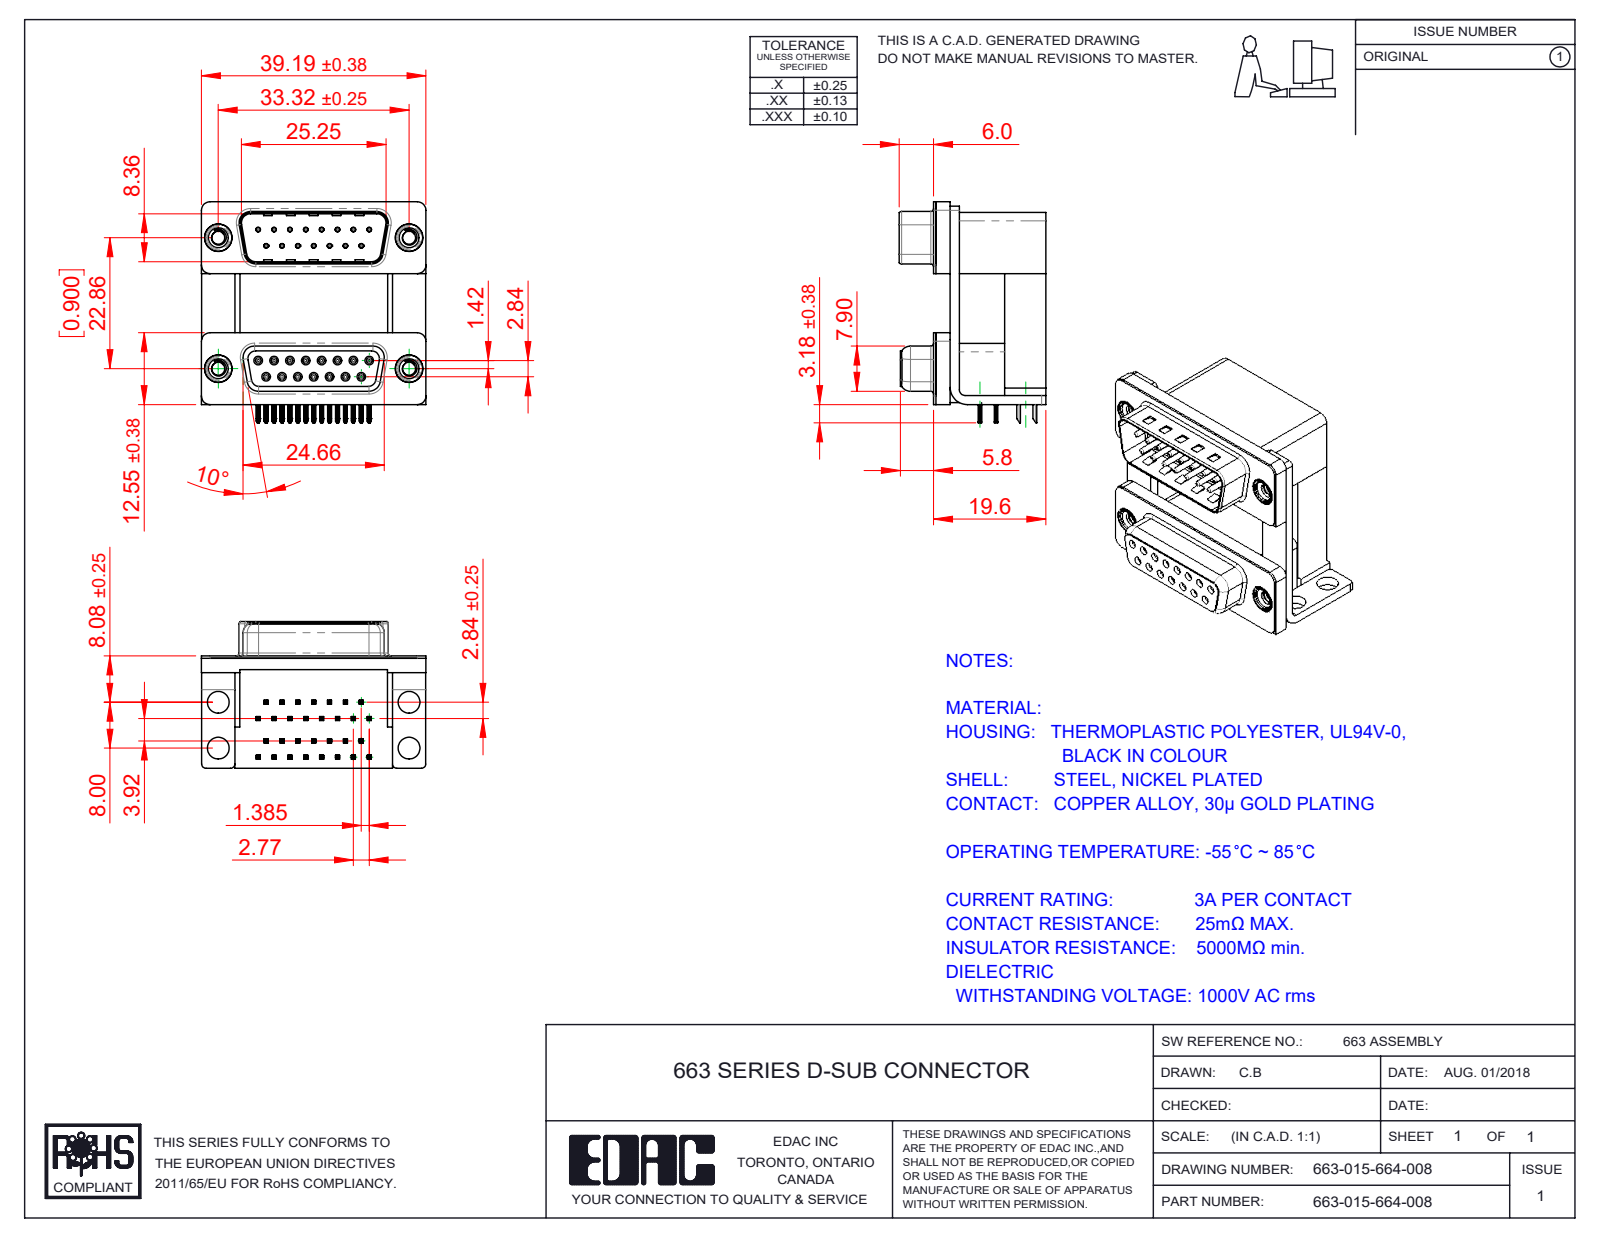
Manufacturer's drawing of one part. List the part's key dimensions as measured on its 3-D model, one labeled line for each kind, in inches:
Part name (STEP PRODUCT): 663 Housing Upper_15 Contacts H; 663 Contact Bottom Upper_H; 663 Mounting Bracket_NoneH; 663 Shell Plug_15 Contacts (+8 more)
STEP written by: SolidWorks 2020 (CONFIG_CONTROL_DESIGN)
Units: inches
Bodies: 41 solids, 3912 faces (2015 planar, 1014 cylindrical, 883 other)
Overall size (bounding box): 1.543 × 1.519 × 1.008
Volume: 0.975 in³ · Surface area: 26.98 in²
Round holes (diameter × count): ⌀0.031 ×30, ⌀0.014 ×15, ⌀0.035 ×15, ⌀0.089 ×4, ⌀0.138 ×4, ⌀0.15 ×4, ⌀0.157 ×4, ⌀0.189 ×4, ⌀0.197 ×4
Round bosses / shafts (diameter × count): ⌀0.047 ×15, ⌀0.03 ×15, ⌀0.193 ×4, ⌀0.187 ×4, ⌀0.154 ×4
Partial cylindrical surfaces — rounded edges, fillets, slot ends (radius × count): R0.004 ×120, R0.006 ×60, R0.01 ×60, R0.005 ×30, R0.014 ×30, R0.059 ×16, R0.013 ×15, R0.02 ×12
Main face-to-face distances: 0.756, 0.016, 0.472, 0.283, 0.657, 0.374, 0.098, 0.421, 0.488, 0.9
Hole centre spacings: 0.124, 0.907, 0.109, 0.926, 0.218, 0.327, 0.9, 0.957
